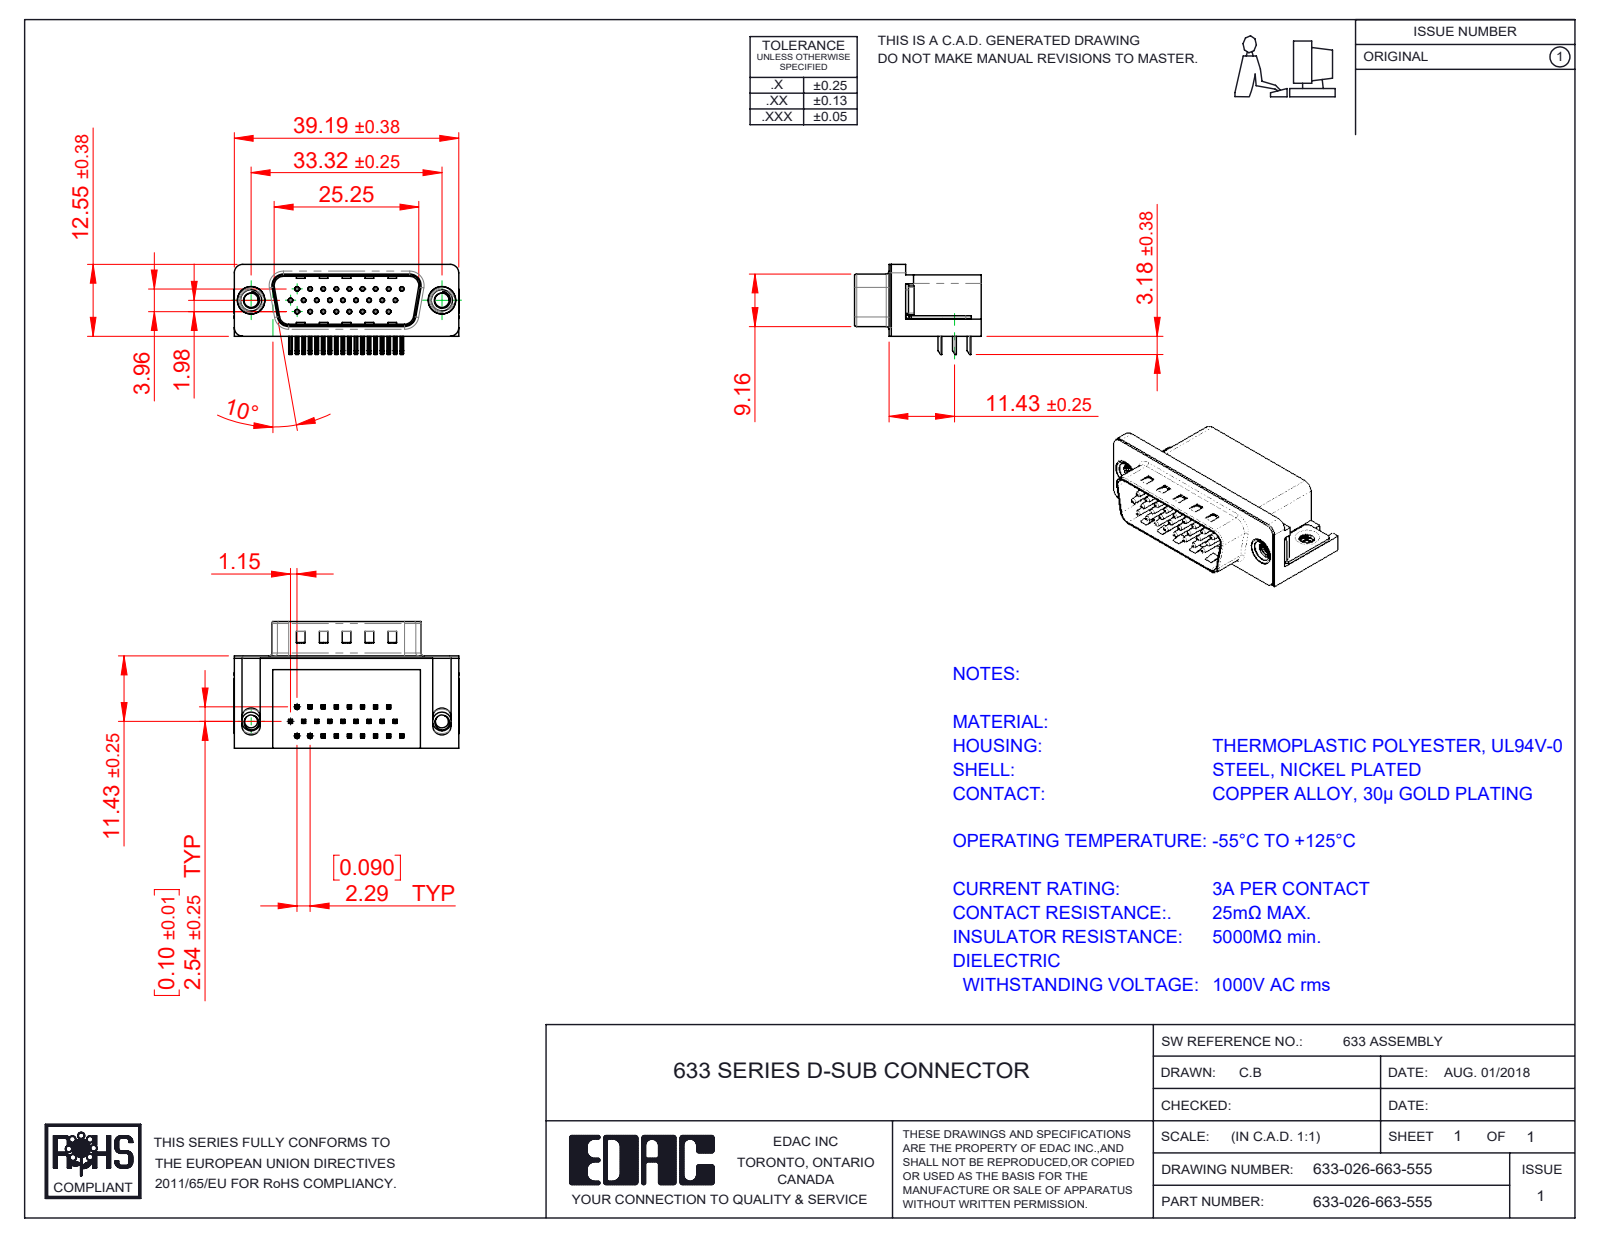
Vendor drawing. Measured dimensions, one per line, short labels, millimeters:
name: 633-026-663-555; 633 4-40 Threaded Board Mount; 633 Contact Bottom; 633 Housing_26 Contact (+4 more)
written by: SolidWorks 2016 (CONFIG_CONTROL_DESIGN)
unit: mm
bodies: 32 solids, 2334 faces (1421 planar, 694 cylindrical, 219 other)
size: 39.22 × 22.1 × 15.73
volume: 5 604 mm³; area: 7 333 mm²
holes: 26× ⌀0.35, 26× ⌀0.8, 2× ⌀2.26, 2× ⌀2.5, 2× ⌀4, 2× ⌀4.8, 2× ⌀5
bosses: 26× ⌀0.75, 2× ⌀4.9, 2× ⌀4.75, 2× ⌀3.9, 2× ⌀3.26
rounds: 112× R0.25, 52× R0.12, 16× R1, 9× R0.5, 8× R1.5, 8× R1.6, 4× R0.9, 4× R2
face distances: 0.4, 10.35, 15.7, 2.9, 2.5, 16.1, 8.76, 0.35, 10.7, 0.5
hole spacings: 2.29, 4.57, 2.28, 3.96, 6.05, 4.58, 6.86, 7.92
